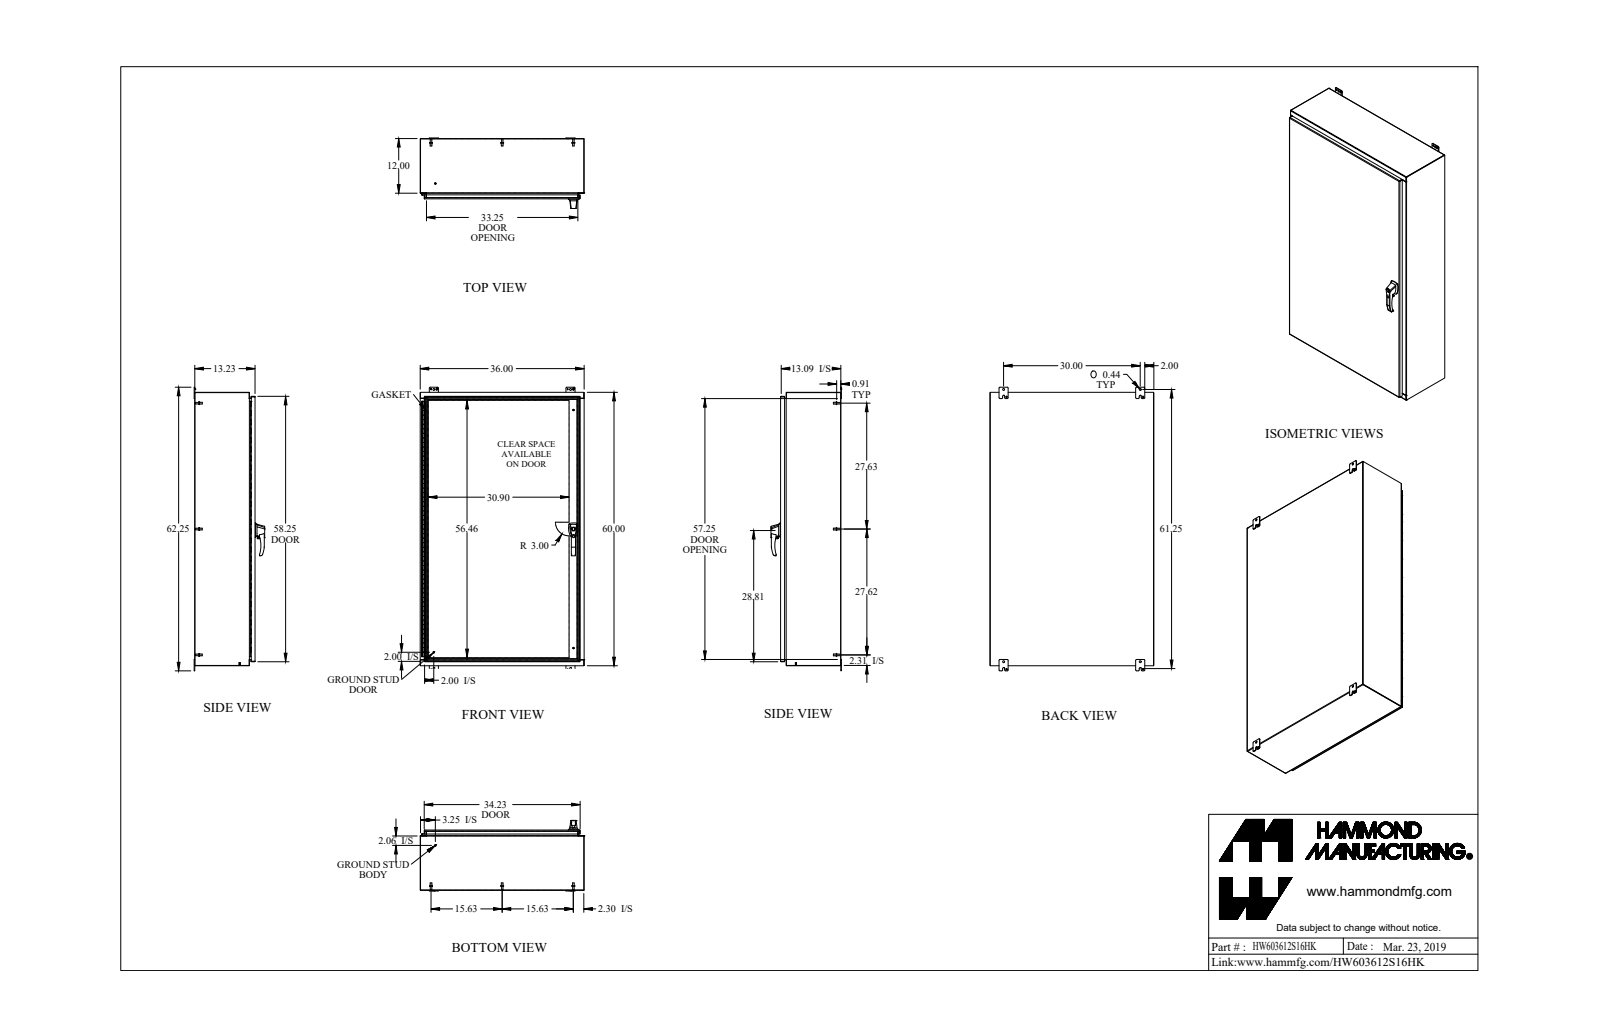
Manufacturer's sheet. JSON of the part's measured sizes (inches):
{"part_name": "HW603612S16HK", "step_written_by": "SolidWorks 2018 (AUTOMOTIVE_DESIGN)", "units": "inches", "bodies": {"solids": 54, "faces": 1985, "planar": 923, "cylindrical": 792, "other": 270}, "overall_size": [62.25, 36, 15.473], "volume_in3": 609.6, "surface_area_in2": 15173, "round_holes": [[0.176, 6], [0.313, 4], [0.437, 4], [0.25, 3], [0.265, 3], [0.413, 3], [0.196, 2], [0.256, 2], [0.394, 2], [0.11, 1], [0.233, 1], [0.307, 1]], "round_bosses_or_shafts": [[0.375, 13], [0.65, 8], [0.332, 8], [0.25, 7], [0.156, 6], [1, 3], [0.63, 2], [0.51, 2]], "partial_cylinders_radius": [[0.25, 27], [0.188, 24], [0.036, 14], [0.108, 14], [0.06, 12], [0.375, 11], [0.125, 9], [0.218, 8]], "face_to_face_distances": [0.072, 13.138, 13.066, 0.095, 13.233, 13.161, 35.928, 59.928, 35.856, 36], "hole_center_spacings": [30, 26.118, 26.119, 52.237, 1.11, 1.111, 1.736, 26.119]}
